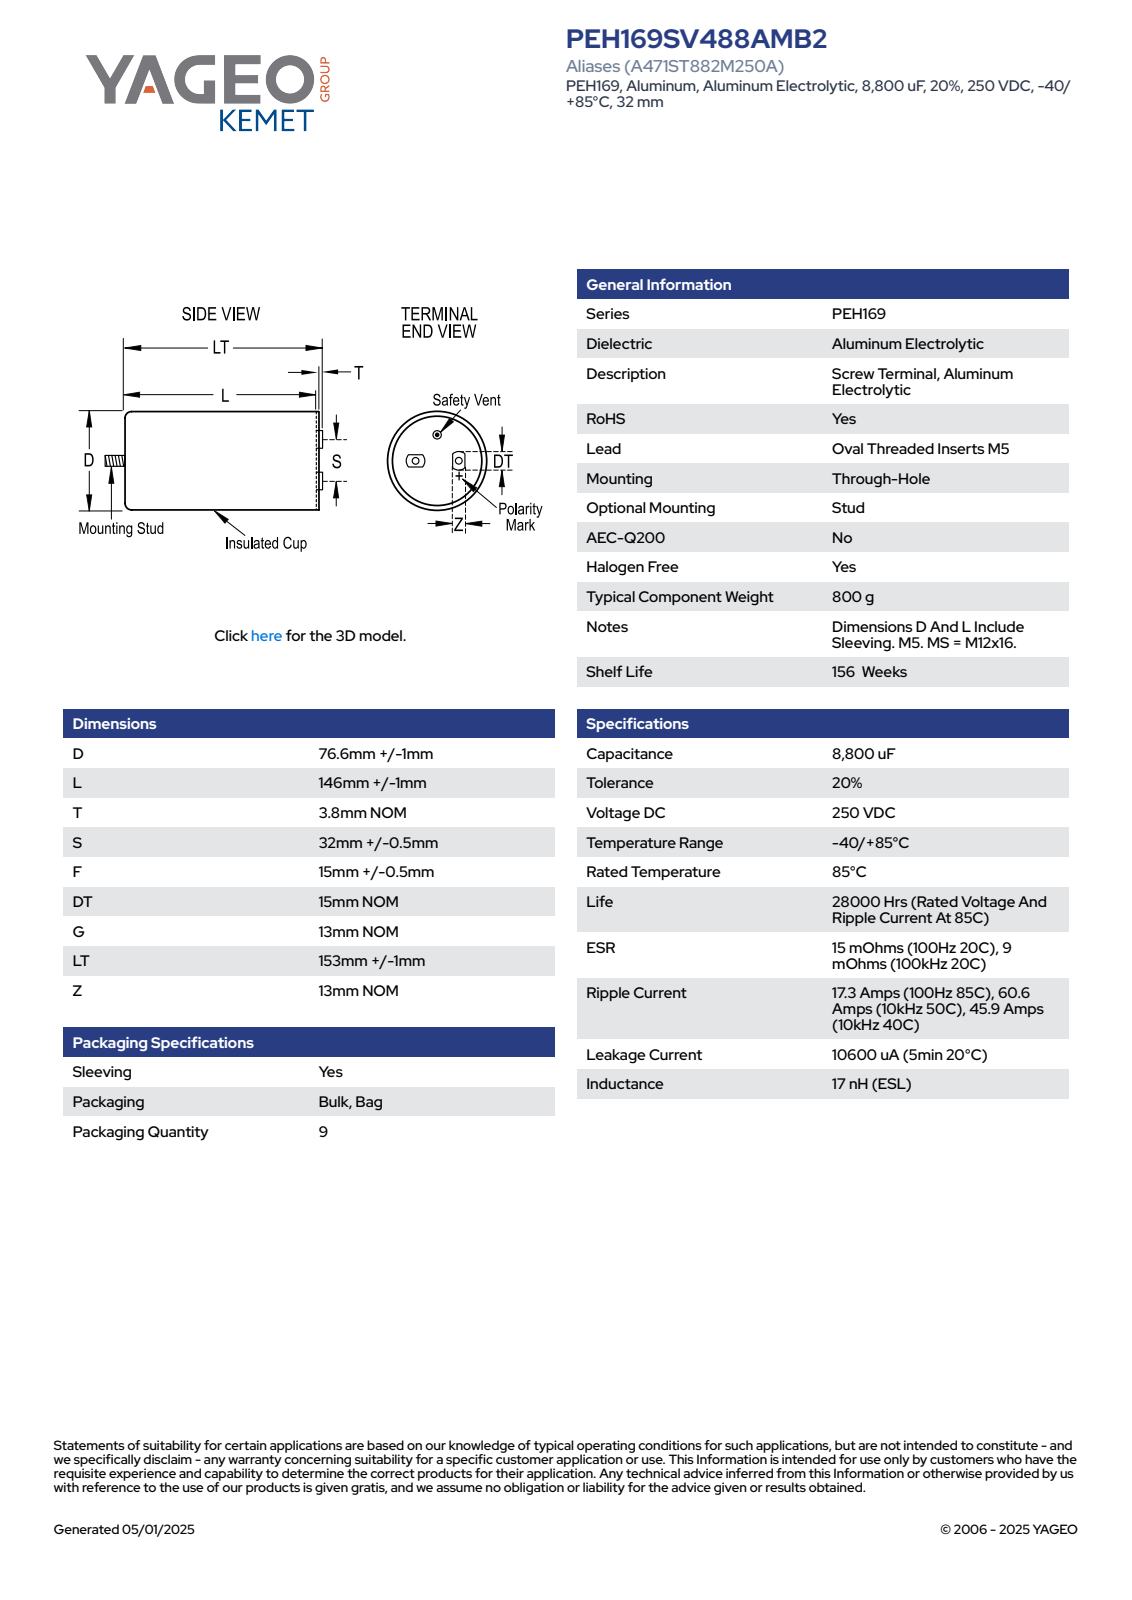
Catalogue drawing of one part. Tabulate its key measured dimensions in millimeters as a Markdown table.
| quantity | value |
| --- | --- |
| part name | CARCS_D77.6L147S32T3.8; Can_21; Oval_Terminal_21; Stud |
| STEP written by | SolidWorks 2014 (AUTOMOTIVE_DESIGN) |
| units | millimeters |
| bodies | 4 solids, 185 faces (70 planar, 83 cylindrical, 32 other) |
| overall size | 170 × 77.6 × 77.6 |
| volume | 699 516 mm³ |
| surface area | 49 240 mm² |
| round holes (diameter × count) | 4.02 × 2, 75.6 × 1 |
| round bosses / shafts (diameter × count) | 7.5 × 2, 77.6 × 1, 12 × 1, 11.6 × 1 |
| partial cylindrical surfaces (radius × count) | 7.5 × 2, 38.79 × 1 |
| main face-to-face distances | 147, 7, 154, 3.2, 3.8, 150.2, 5, 170, 166.2, 163 |
| hole center spacings | 16, 32 |
